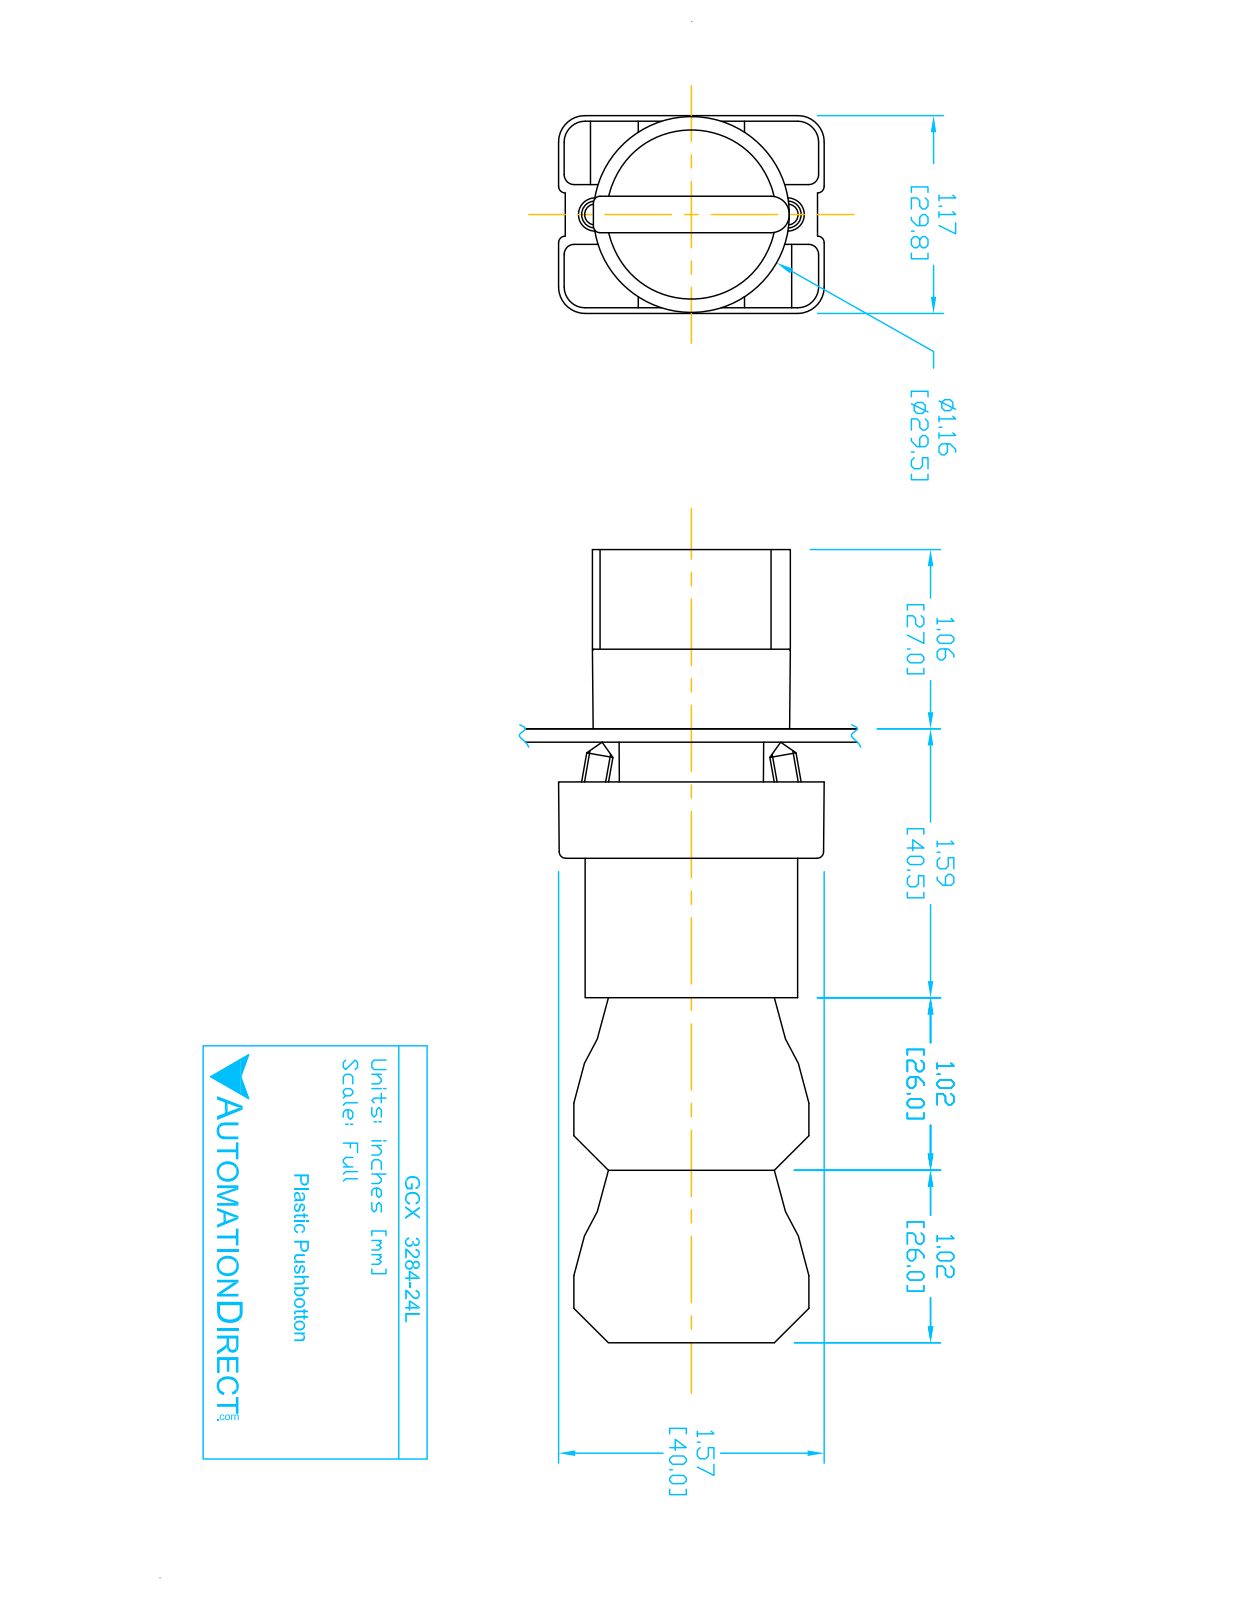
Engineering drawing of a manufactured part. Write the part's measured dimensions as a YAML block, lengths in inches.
part_name: "ECX3029-2; ecx1040; ECX1050; ecx1030 (+2 more)"
step_written_by: "SolidWorks 2016 (AUTOMOTIVE_DESIGN)"
units: inches
bodies: {solids: 11, faces: 724, planar: 488, cylindrical: 193, other: 43}
overall_size: [4.677, 1.581, 1.177]
volume: 4.751
surface_area: 59.22
round_holes:
  - {diameter: 0.079, count: 4}
  - {diameter: 0.087, count: 2}
  - {diameter: 0.124, count: 2}
  - {diameter: 0.13, count: 2}
  - {diameter: 0.197, count: 1}
  - {diameter: 0.469, count: 1}
  - {diameter: 0.878, count: 1}
  - {diameter: 0.888, count: 1}
  - {diameter: 1.024, count: 1}
round_bosses_or_shafts:
  - {diameter: 0.157, count: 4}
  - {diameter: 1.175, count: 1}
  - {diameter: 1.004, count: 1}
  - {diameter: 0.945, count: 1}
  - {diameter: 0.856, count: 1}
  - {diameter: 0.78, count: 1}
  - {diameter: 0.504, count: 1}
partial_cylinders:
  - {radius: 0.059, count: 24}
  - {radius: 0.041, count: 12}
  - {radius: 0.124, count: 12}
  - {radius: 0.157, count: 12}
  - {radius: 0.039, count: 9}
  - {radius: 0.02, count: 2}
  - {radius: 0.063, count: 2}
  - {radius: 0.079, count: 2}
face_to_face_distances: [0.579, 0.593, 1.024, 1.171, 0.014, 0.827, 1.85, 3.043, 2.02, 1.193]
hole_center_spacings: [0.236, 1.003, 0.974, 0.472, 0.539, 0.544, 1.083, 0.484]
